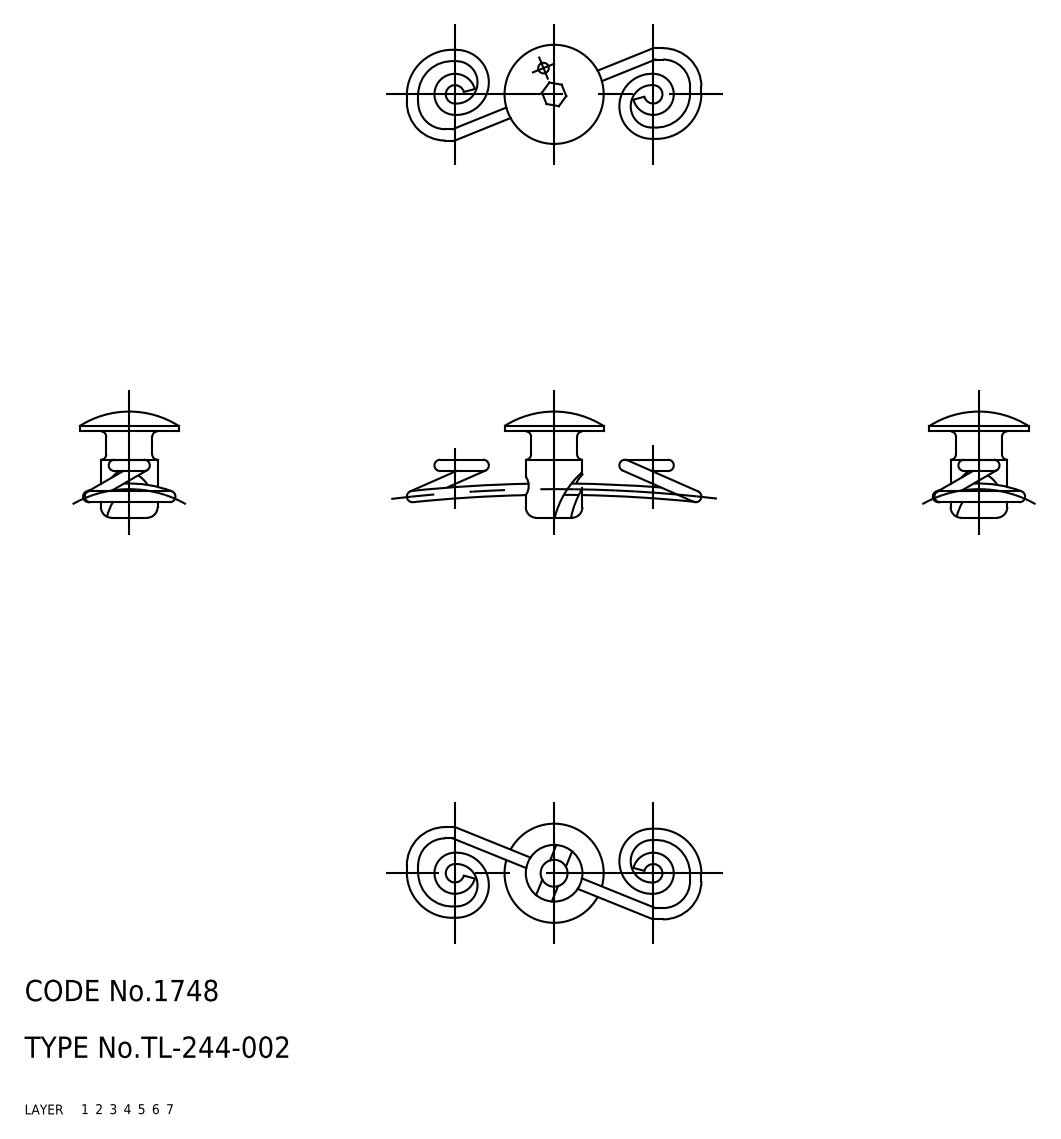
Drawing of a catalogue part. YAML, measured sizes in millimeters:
part_name: "spring; fastener; TL_244_002_32137_36"
step_written_by: "CADfix (AUTOMOTIVE_DESIGN)"
units: millimeters
bodies: {solids: 2, faces: 60, planar: 0, cylindrical: 0, other: 60}
overall_size: [41.6, 14.91, 14]
volume: 855
surface_area: 1327
